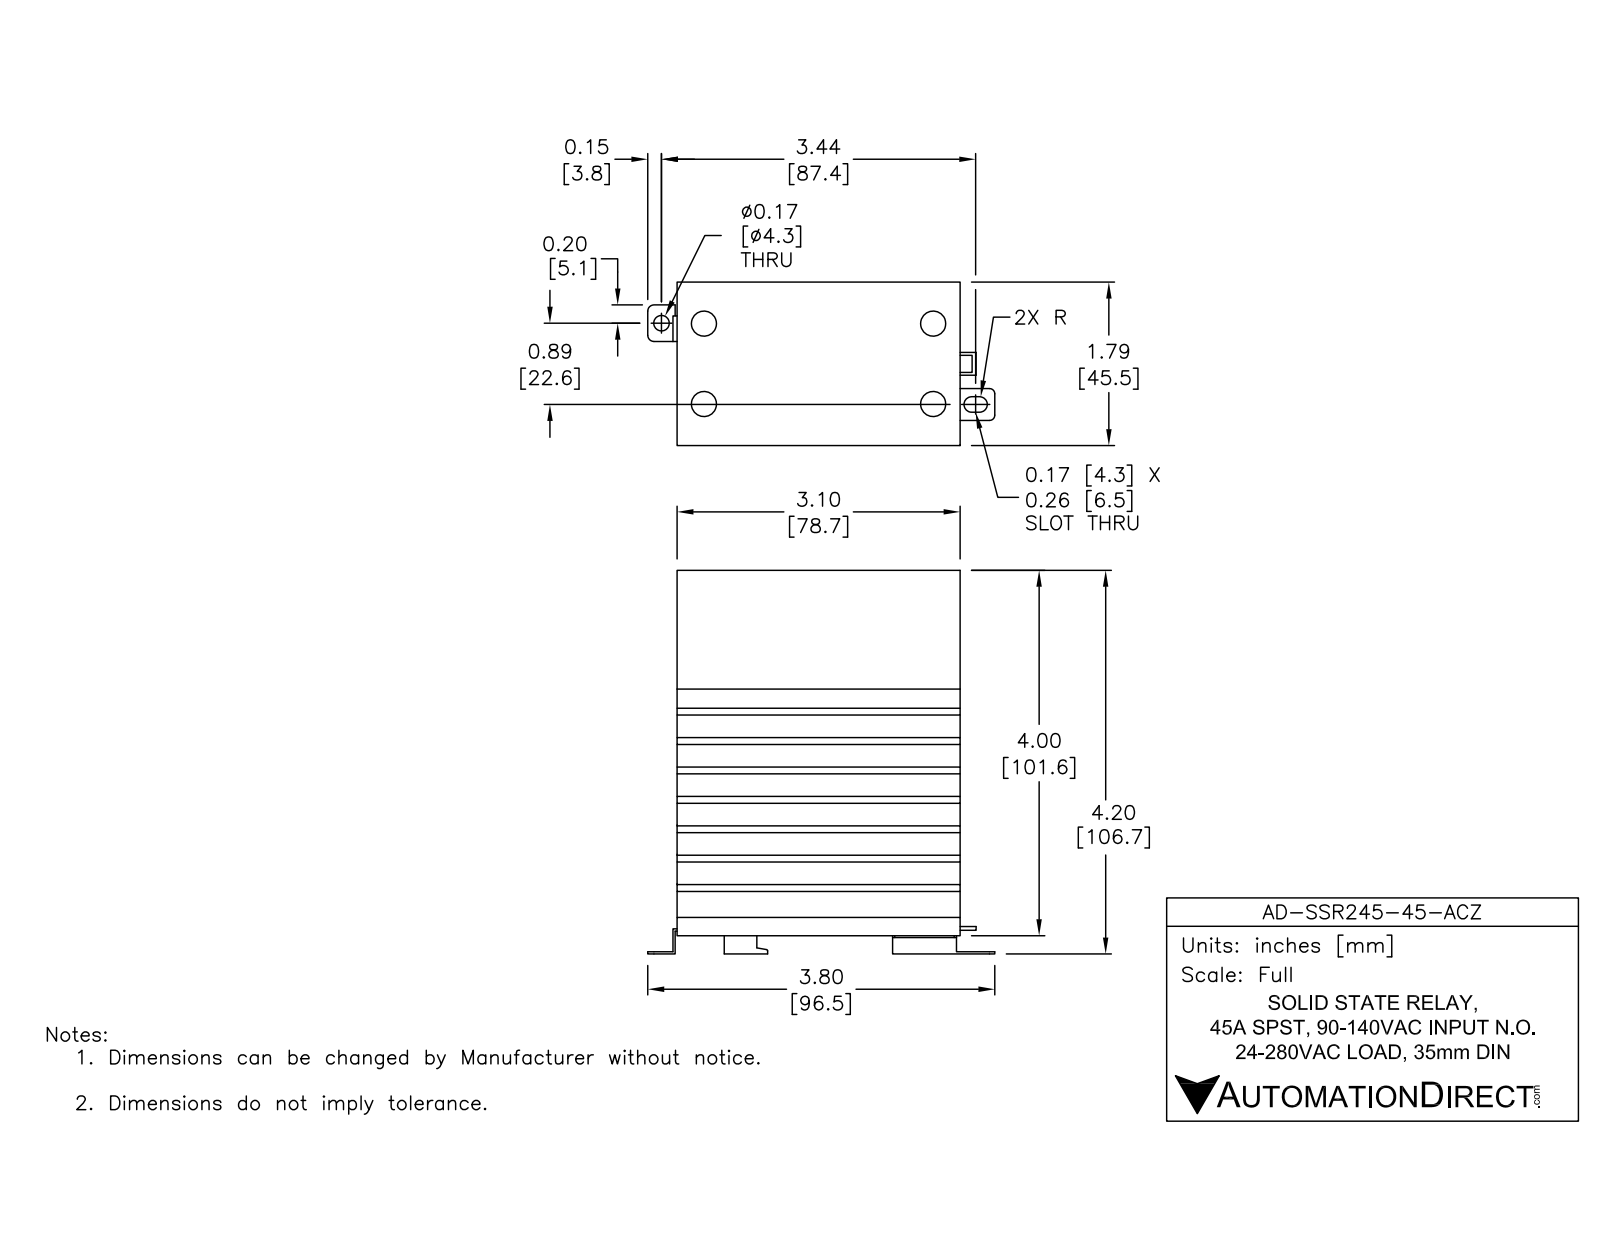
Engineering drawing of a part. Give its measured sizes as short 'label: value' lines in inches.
name: AD-SSR245-45-ACZ
written by: SolidWorks 2014 (AUTOMOTIVE_DESIGN)
unit: in
bodies: 1 solid, 171 faces (151 planar, 20 cylindrical, 0 other)
size: 4.2 × 3.8 × 1.79
volume: 12.46 in³; area: 125.1 in²
holes: 2× ⌀0.275, 2× ⌀0.275, 1× ⌀0.17
rounds: 2× R0.05, 2× R0.058, 2× R0.067, 2× R0.085, 1× R0.015
face distances: 0.644, 0.322, 0.966, 0.397, 0.322, 0.247, 1.609, 0.075, 0.569, 0.075
hole spacings: 0.88, 2.51, 2.66, 0.465, 1, 2.975, 3.104
